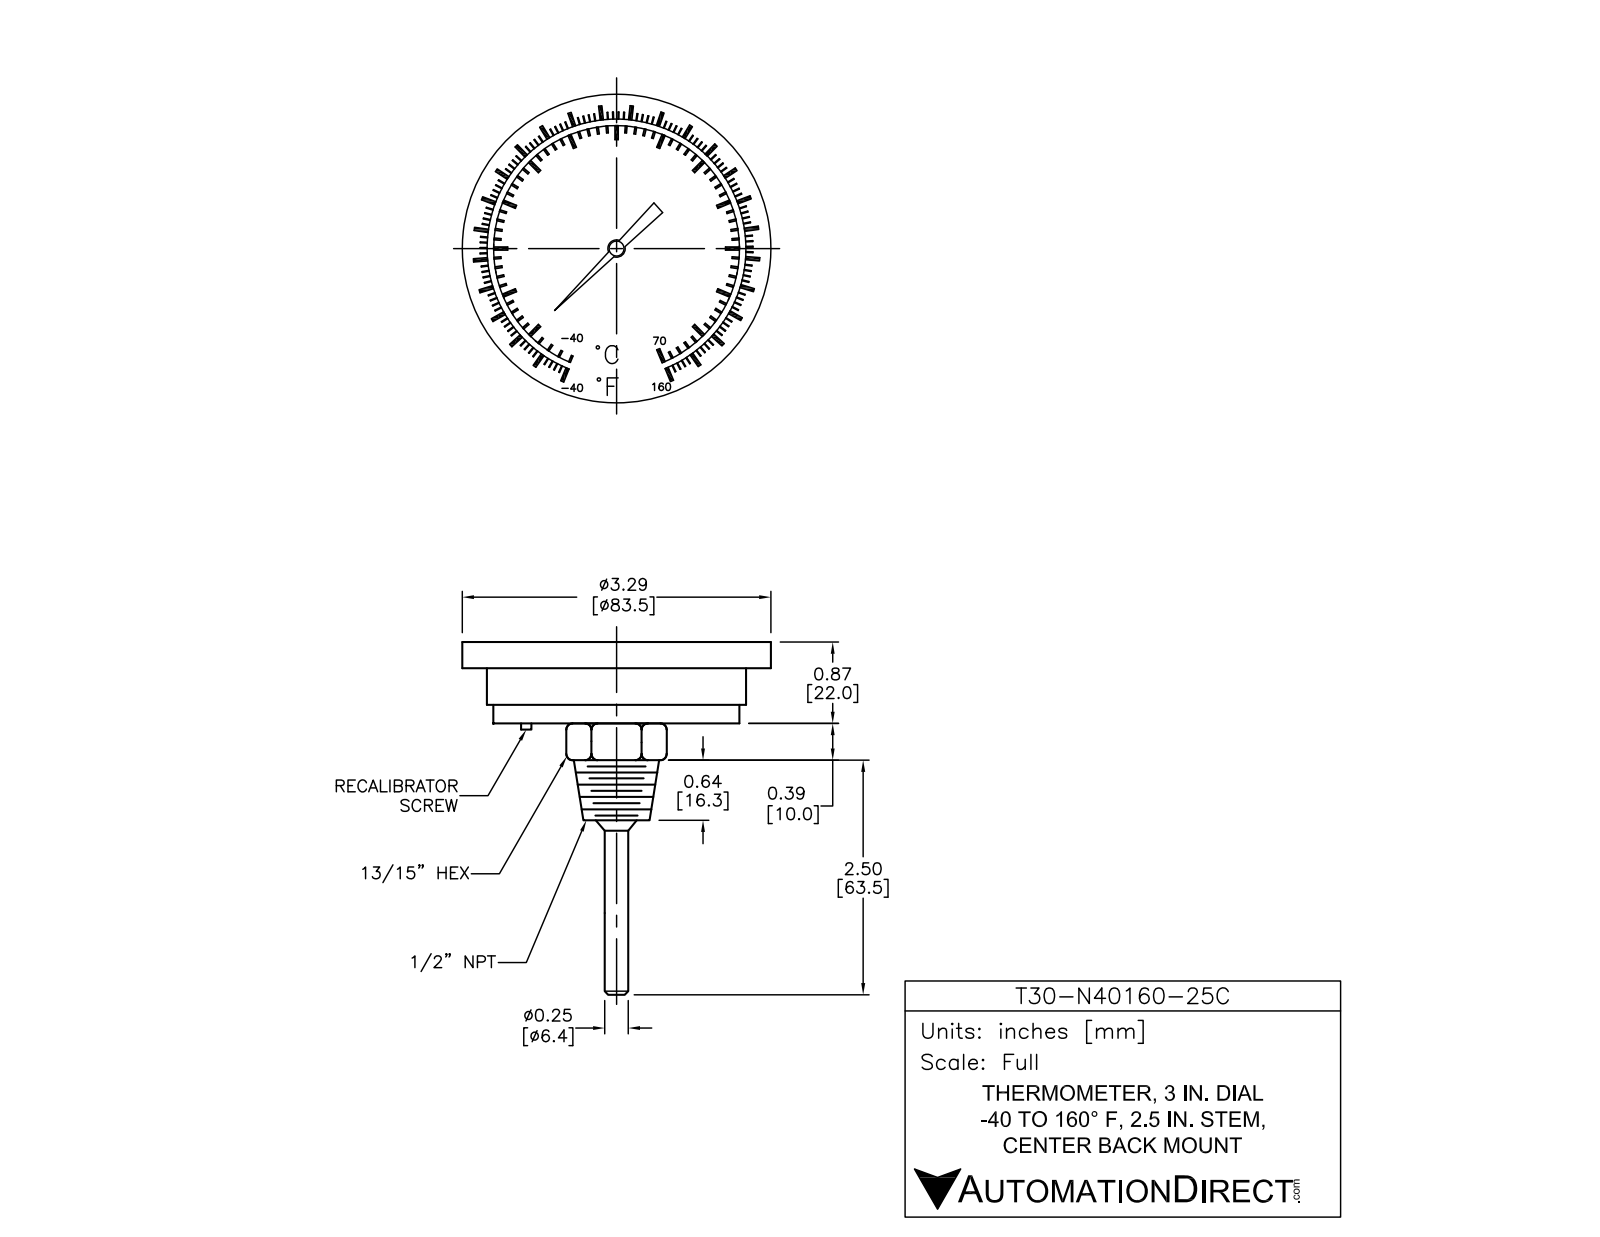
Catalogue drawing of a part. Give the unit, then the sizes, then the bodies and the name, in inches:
Units: inches
Overall size (bounding box): 3.76 × 3.29 × 3.29
Round holes (diameter × count): ⌀0.067 ×1, ⌀2.69 ×1
Round bosses / shafts (diameter × count): ⌀3.29 ×1, ⌀2.76 ×1, ⌀2.62 ×1, ⌀0.846 ×1, ⌀0.258 ×1
Partial cylindrical surfaces — rounded edges, fillets, slot ends (radius × count): R0.04 ×1, R0.709 ×1, R0.859 ×1, R0.969 ×1, R1.119 ×1
Main face-to-face distances: 0.222, 0.078, 0.3, 0.87, 0.648, 0.57, 0.368, 0.59, 0.29, 0.28
Volume: 3.073 in³ · Surface area: 33.03 in²
Bodies: 72 solids, 1258 faces (1113 planar, 85 cylindrical, 60 other)
Part name (STEP PRODUCT): T30-N40160-25C
STEP written by: SolidWorks 2021 (AUTOMOTIVE_DESIGN)
